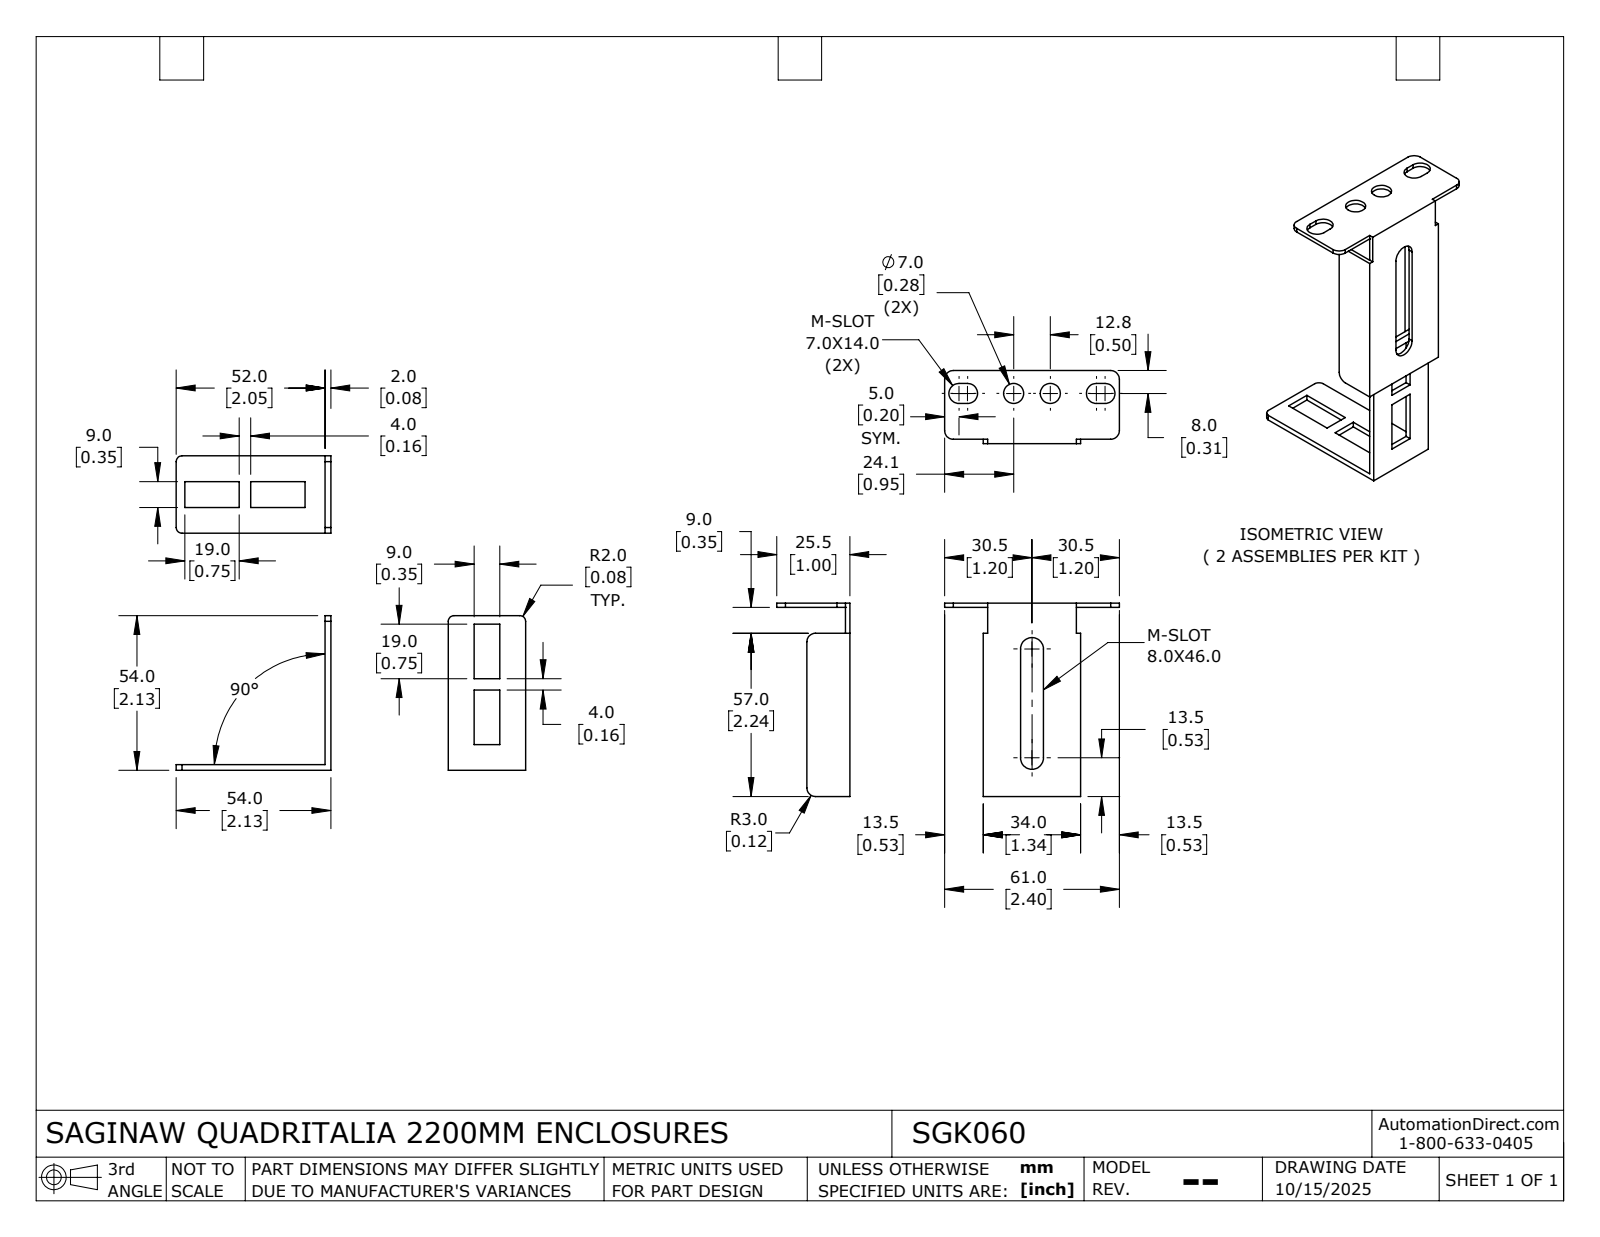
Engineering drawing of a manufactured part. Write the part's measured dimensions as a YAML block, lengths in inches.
part_name: "SGK060"
step_written_by: "SolidWorks 2024 (AUTOMOTIVE_DESIGN)"
units: inches
bodies: {solids: 4, faces: 146, planar: 100, cylindrical: 46, other: 0}
overall_size: [9.362, 4.168, 2.402]
volume: 1.391
surface_area: 48.23
round_holes:
  - {diameter: 0.276, count: 4}
partial_cylinders:
  - {radius: 0.118, count: 12}
  - {radius: 0.138, count: 8}
  - {radius: 0.079, count: 6}
  - {radius: 0.157, count: 2}
face_to_face_distances: [0.059, 0.079, 9.303, 1.28, 0.138, 9.244, 4.109, 4.168, 9.224, 9.165]
hole_center_spacings: [0.504, 7.984, 8]
